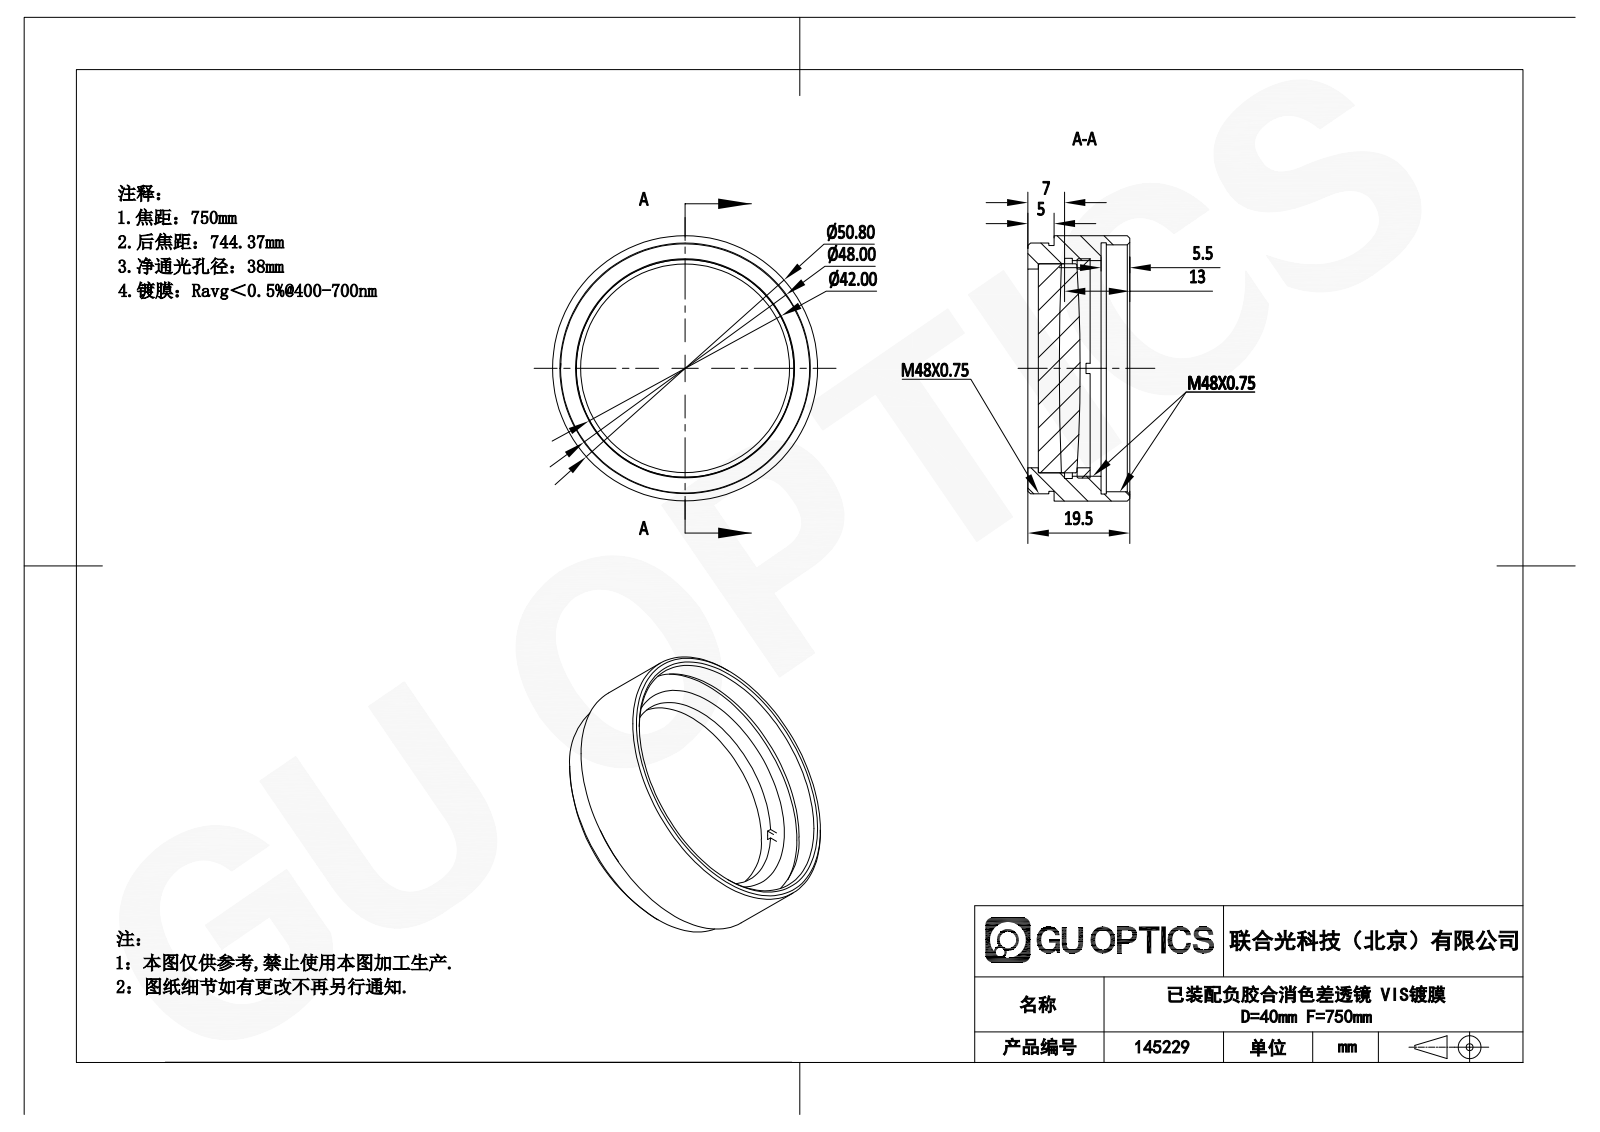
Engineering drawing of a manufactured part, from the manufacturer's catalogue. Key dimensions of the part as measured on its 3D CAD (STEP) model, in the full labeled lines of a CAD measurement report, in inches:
Part name (STEP PRODUCT): M42x0.75ѹȦ; APD-ML40-750-VIS-A; GL31-040-750-VIS_Solidworks
STEP written by: SolidWorks 2022 (AUTOMOTIVE_DESIGN)
Units: inches
Bodies: 4 solids, 64 faces (18 planar, 26 cylindrical, 20 other)
Overall size (bounding box): 2 × 2 × 0.768
Volume: 1.274 in³ · Surface area: 22.85 in²
Round holes (diameter × count): ⌀1.496 ×1, ⌀1.624 ×1, ⌀1.657 ×1, ⌀1.86 ×1, ⌀1.894 ×1
Round bosses / shafts (diameter × count): ⌀2 ×1, ⌀1.89 ×1, ⌀1.85 ×1, ⌀1.654 ×1, ⌀1.575 ×1
Main face-to-face distances: 0.551, 0.197, 0.079, 0.354, 0.276, 0.469, 0.272, 0.082, 0.371, 0.174
